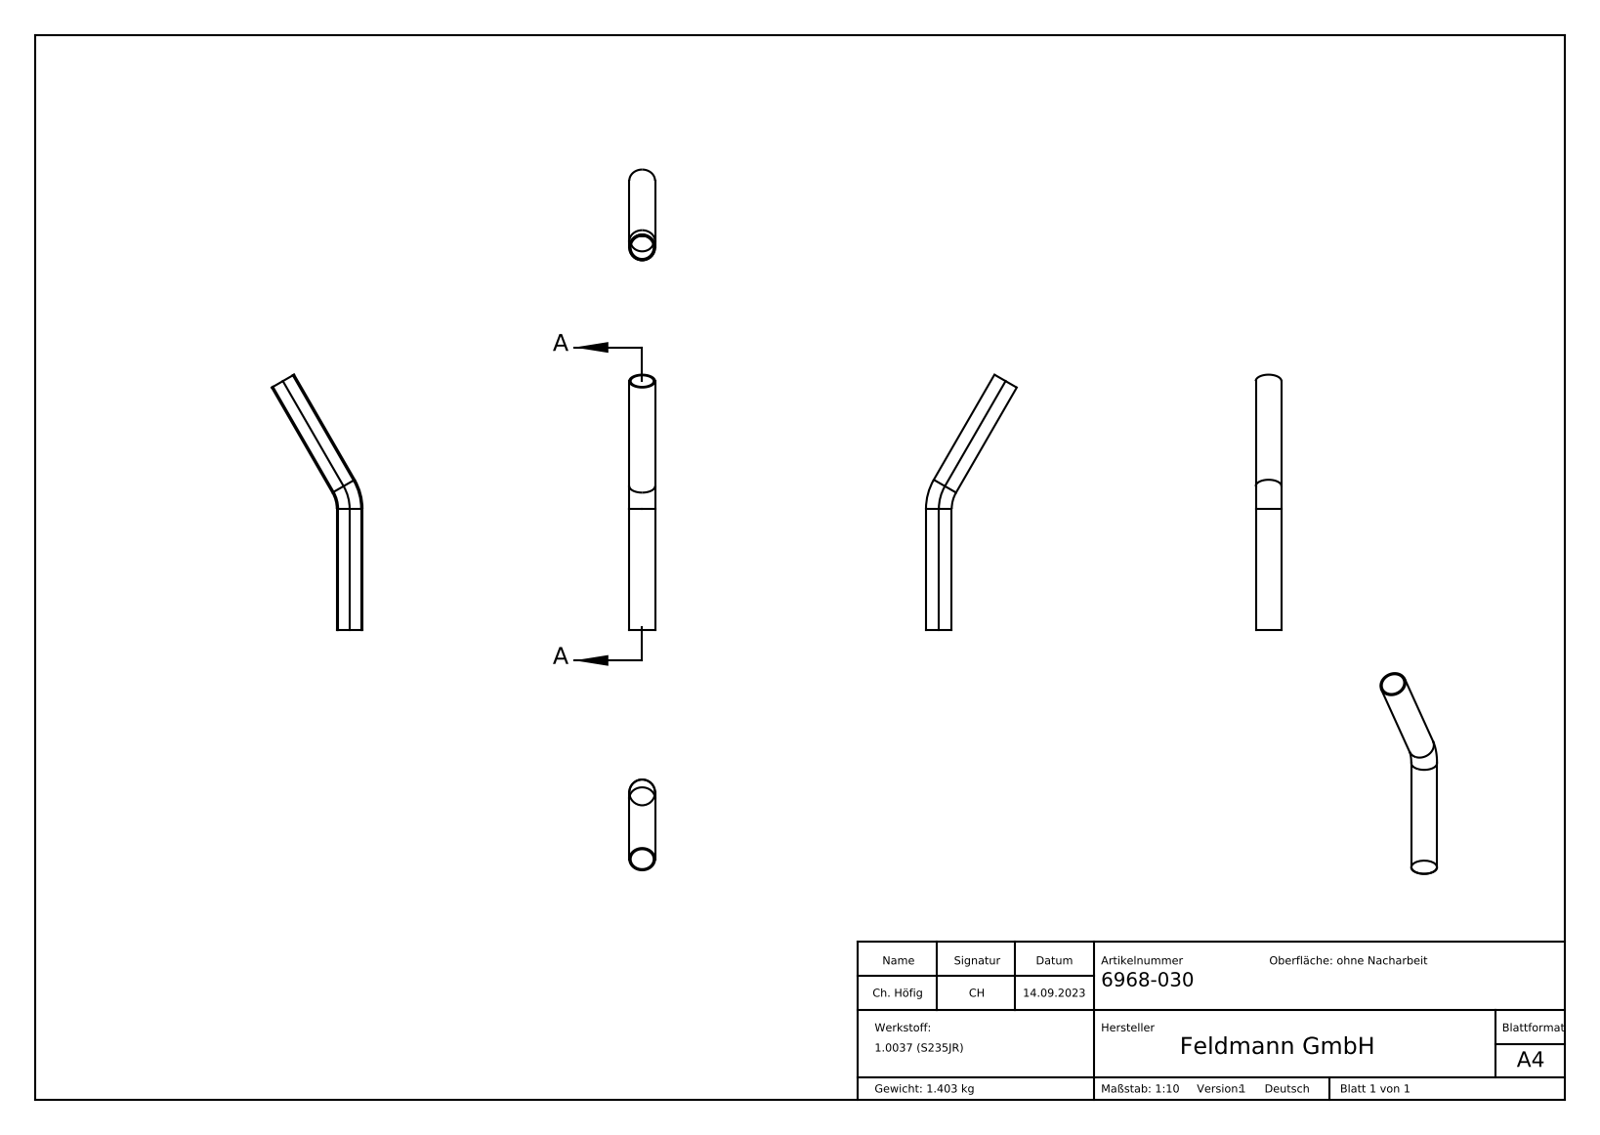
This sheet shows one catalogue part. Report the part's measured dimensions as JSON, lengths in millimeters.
{"part_name": "6968-030", "step_written_by": "SolidWorks 2018 (CONFIG_CONTROL_DESIGN)", "units": "millimeters", "bodies": {"solids": 1, "faces": 228, "planar": 98, "cylindrical": 4, "other": 126}, "overall_size": [479.56, 170.33, 48.3], "volume_mm3": 179856, "surface_area_mm2": 144608, "round_holes": [[43.3, 2]], "round_bosses_or_shafts": [[48.3, 2]], "face_to_face_distances": [0.5, 0.55, 0.53, 0.34, 0.31, 0.45, 0.58, 0.39, 0.48, 0.47]}
